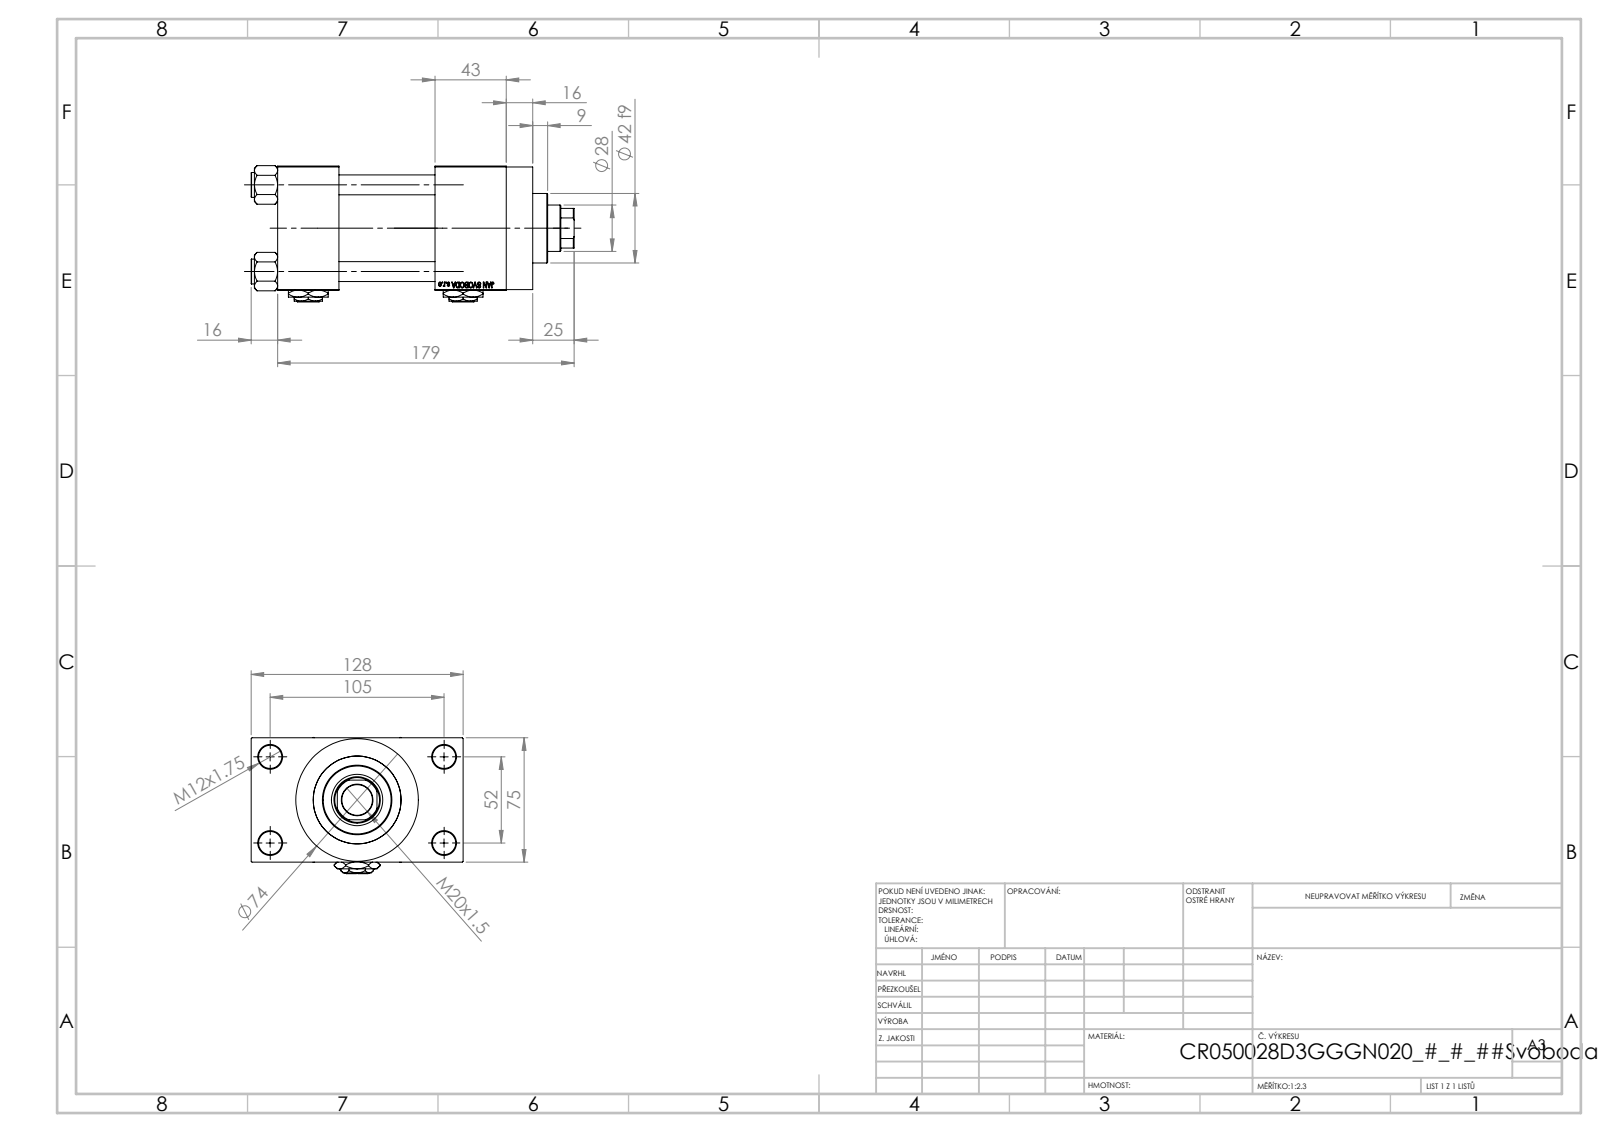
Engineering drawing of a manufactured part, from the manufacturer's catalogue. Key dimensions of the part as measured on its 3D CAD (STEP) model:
Part name (STEP PRODUCT): V215CR_D_TYCINKA; V215CR_D_Body; V215CR_VCP_D; Zatka_pro_OIL_PORT (+2 more)
STEP written by: SolidWorks 2019 (CONFIG_CONTROL_DESIGN)
Units: millimetres
Bodies: 13 solids, 1205 faces (545 planar, 100 cylindrical, 560 other)
Overall size (bounding box): 195 × 128 × 82.27
Volume: 810 868 mm³ · Surface area: 173 104 mm²
Round holes (diameter × count): ⌀12 ×4, ⌀14 ×4, ⌀7 ×2, ⌀20.96 ×2, ⌀30 ×2, ⌀18.5 ×1, ⌀28 ×1, ⌀31 ×1, ⌀41 ×1, ⌀50 ×1, ⌀53 ×1
Round bosses / shafts (diameter × count): ⌀15 ×4, ⌀74 ×1, ⌀56 ×1, ⌀42 ×1
Partial cylindrical surfaces — rounded edges, fillets, slot ends (radius × count): R13.5 ×1
Main face-to-face distances: 75, 58, 37, 95, 101.5, 26.5, 138, 101, 43, 16
Hole centre spacings: 26.35, 36.98, 52.3, 58.43, 58.59, 78.65, 94.37, 52
